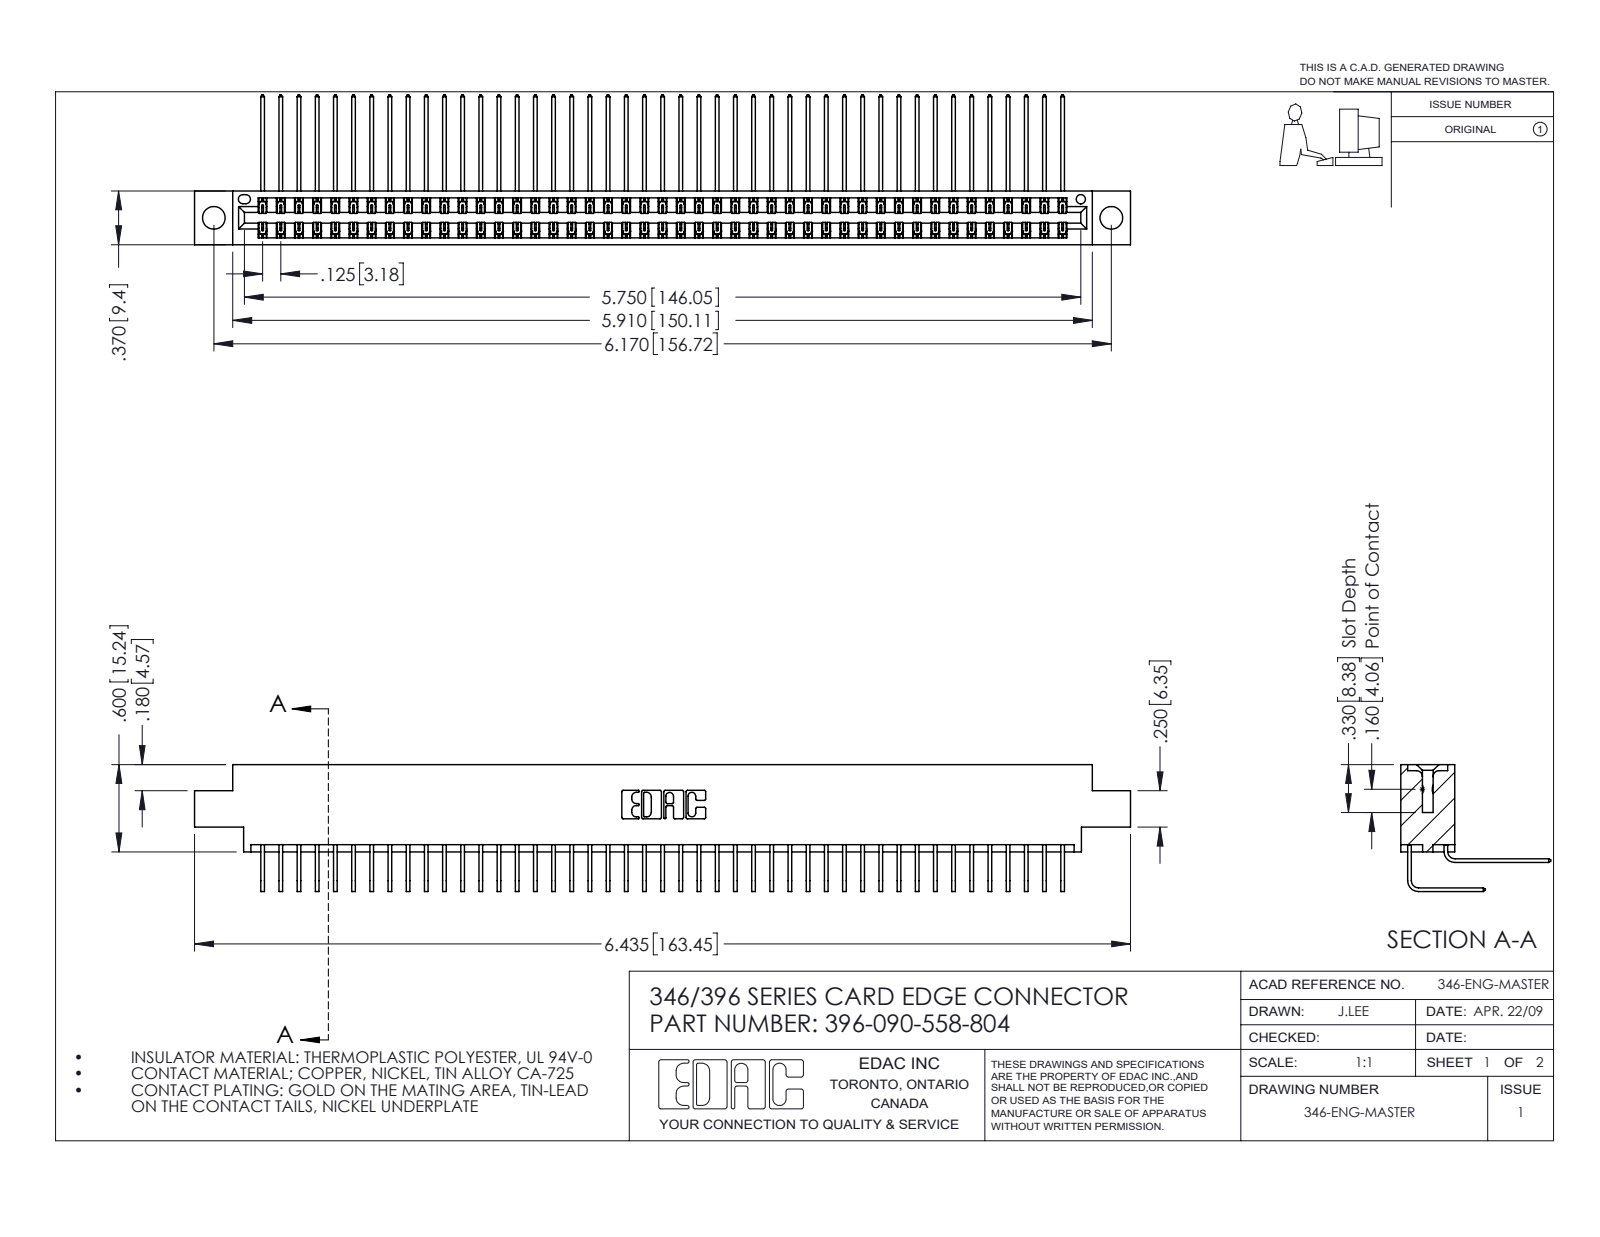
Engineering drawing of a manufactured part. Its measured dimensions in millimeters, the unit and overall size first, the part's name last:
Units: millimetres
Overall size (bounding box): 163.4 × 26.2 × 22.2
Round holes (diameter × count): ⌀4 ×2, ⌀1.6 ×1
Partial cylindrical surfaces — rounded edges, fillets, slot ends (radius × count): R0.2 ×135, R0.3 ×22, R0.2 ×6, R0.8 ×6, R0.7 ×3, R0.4 ×2, R0.6 ×2, R0.6 ×2
Main face-to-face distances: 8.2, 1.2, 0.6, 9.4, 6.4, 7.6, 1.8, 7, 3.8, 5.6
Hole centre spacings: 6.2, 151.4, 156.7
Volume: 16 200 mm³ · Surface area: 24 850 mm²
Bodies: 91 solids, 4986 faces (3410 planar, 1576 cylindrical, 0 other)
Part name (STEP PRODUCT): 346 Part_0.170 Offset - 0.156 Dia-TH; 345-292-001_558 Tail - 2; 345-292-001_558 559 Tail - 1; 396-090-558-804
STEP written by: SolidWorks 2016 (CONFIG_CONTROL_DESIGN)
